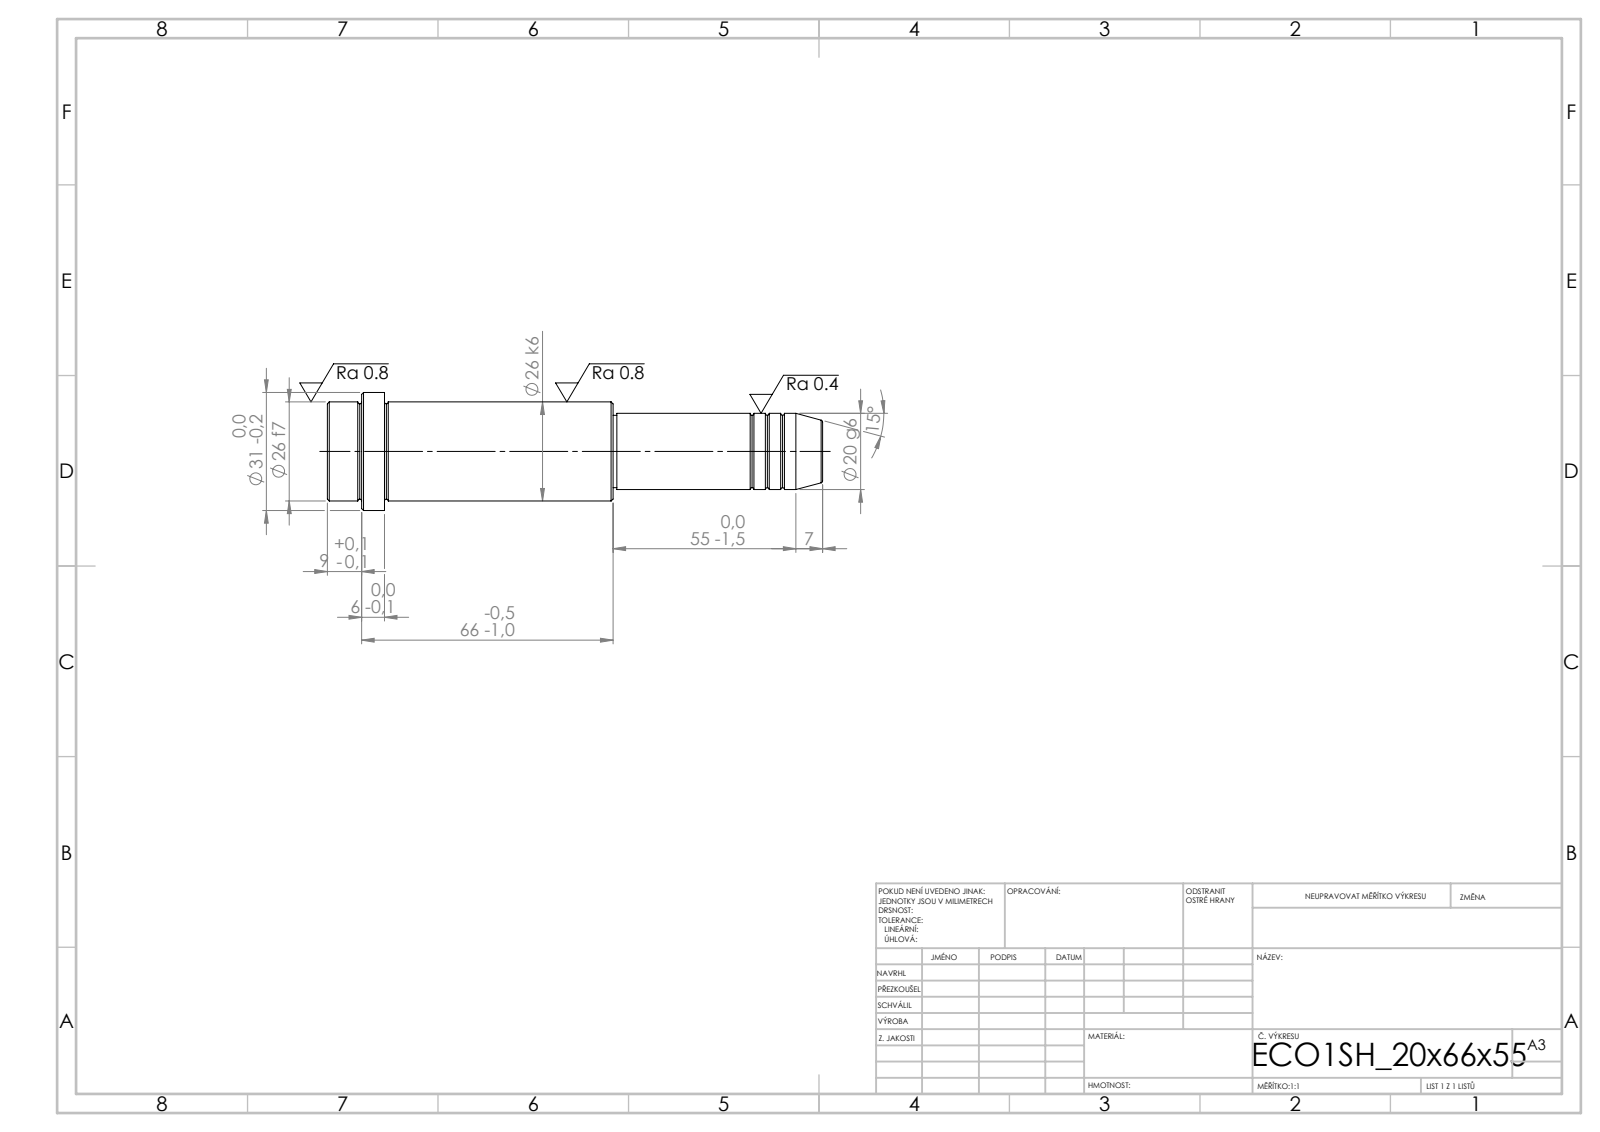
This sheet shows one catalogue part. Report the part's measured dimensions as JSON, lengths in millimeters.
{"step_written_by": "SolidWorks 2019 (CONFIG_CONTROL_DESIGN)", "units": "millimeters", "bodies": {"solids": 1, "faces": 52, "planar": 6, "cylindrical": 16, "other": 30}, "overall_size": [130, 31, 31], "volume_mm3": 57855, "surface_area_mm2": 11212, "round_bosses_or_shafts": [[31, 1], [26, 1], [20, 1], [19, 1]], "face_to_face_distances": [15, 60, 75, 55, 115, 130, 121, 66, 6, 9]}
